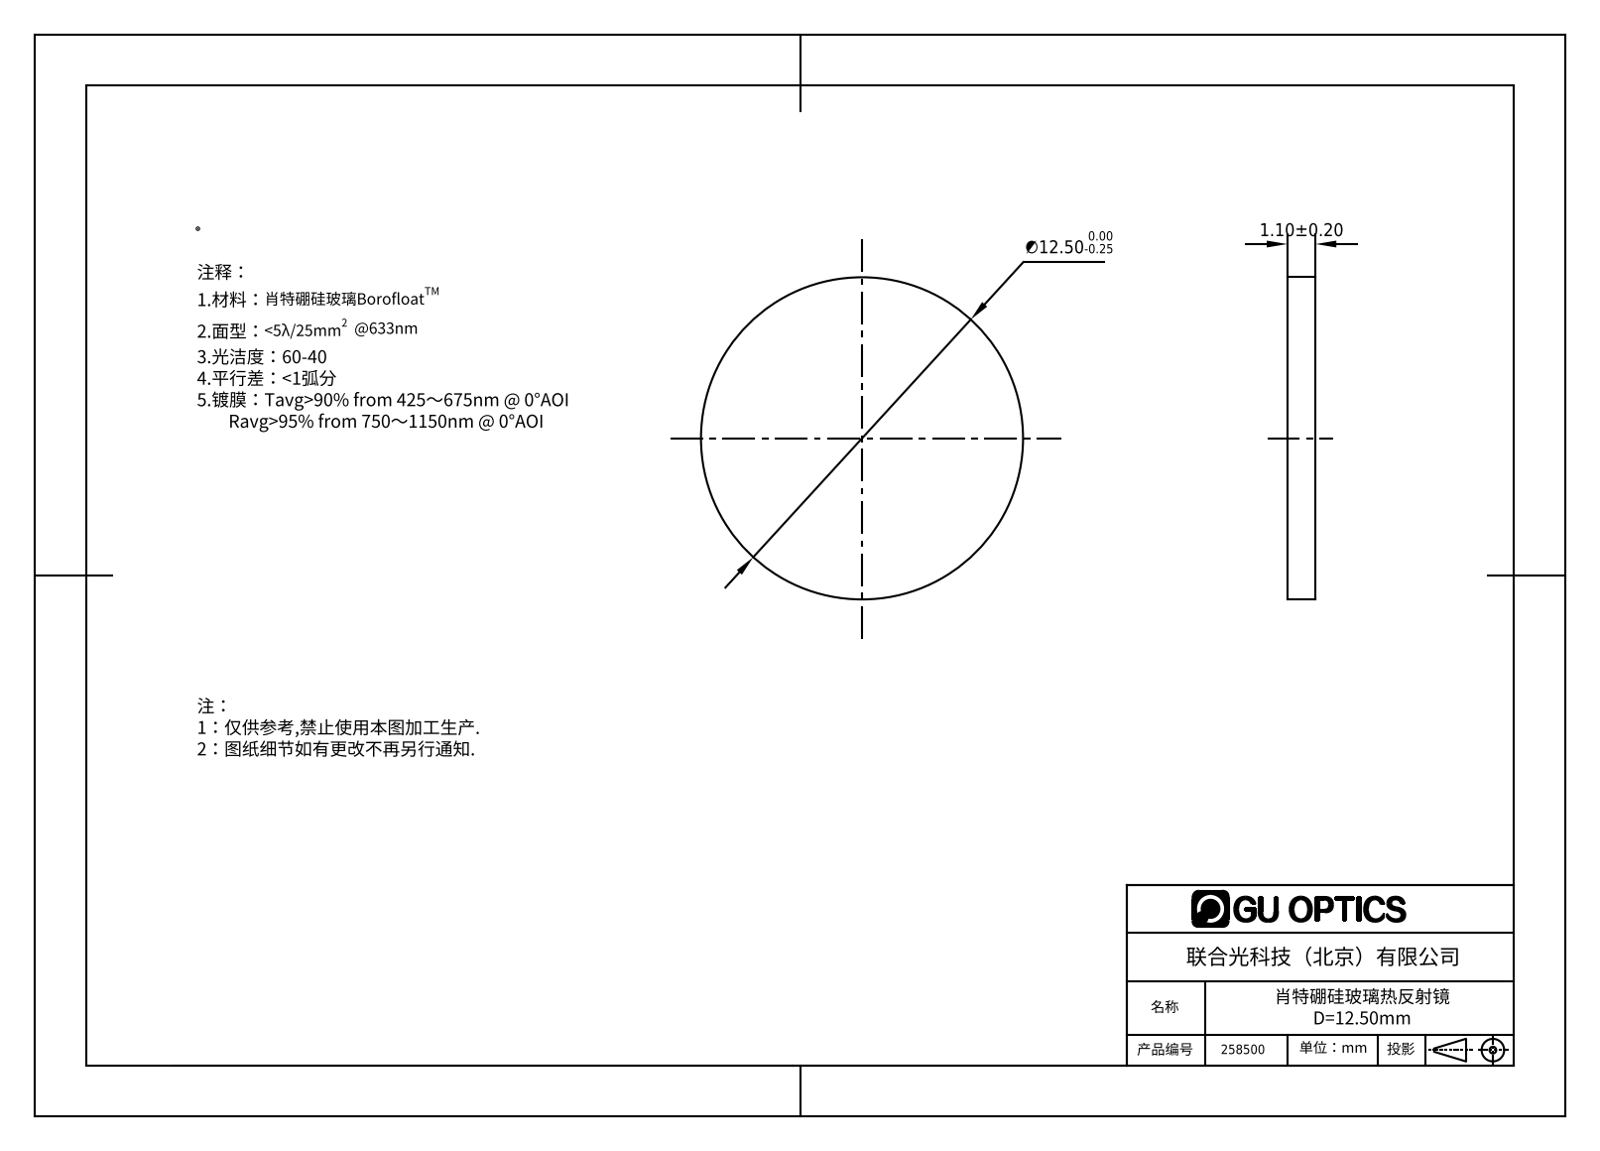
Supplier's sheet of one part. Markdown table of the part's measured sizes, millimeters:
| quantity | value |
| --- | --- |
| part name | 258500 |
| STEP written by | SolidWorks 2016 (AUTOMOTIVE_DESIGN) |
| units | millimeters |
| bodies | 1 solid, 4 faces (2 planar, 2 cylindrical, 0 other) |
| overall size | 12.5 × 12.5 × 1.1 |
| volume | 135 mm³ |
| surface area | 289 mm² |
| round bosses / shafts (diameter × count) | 12.5 × 1 |
| main face-to-face distances | 1.1 |
